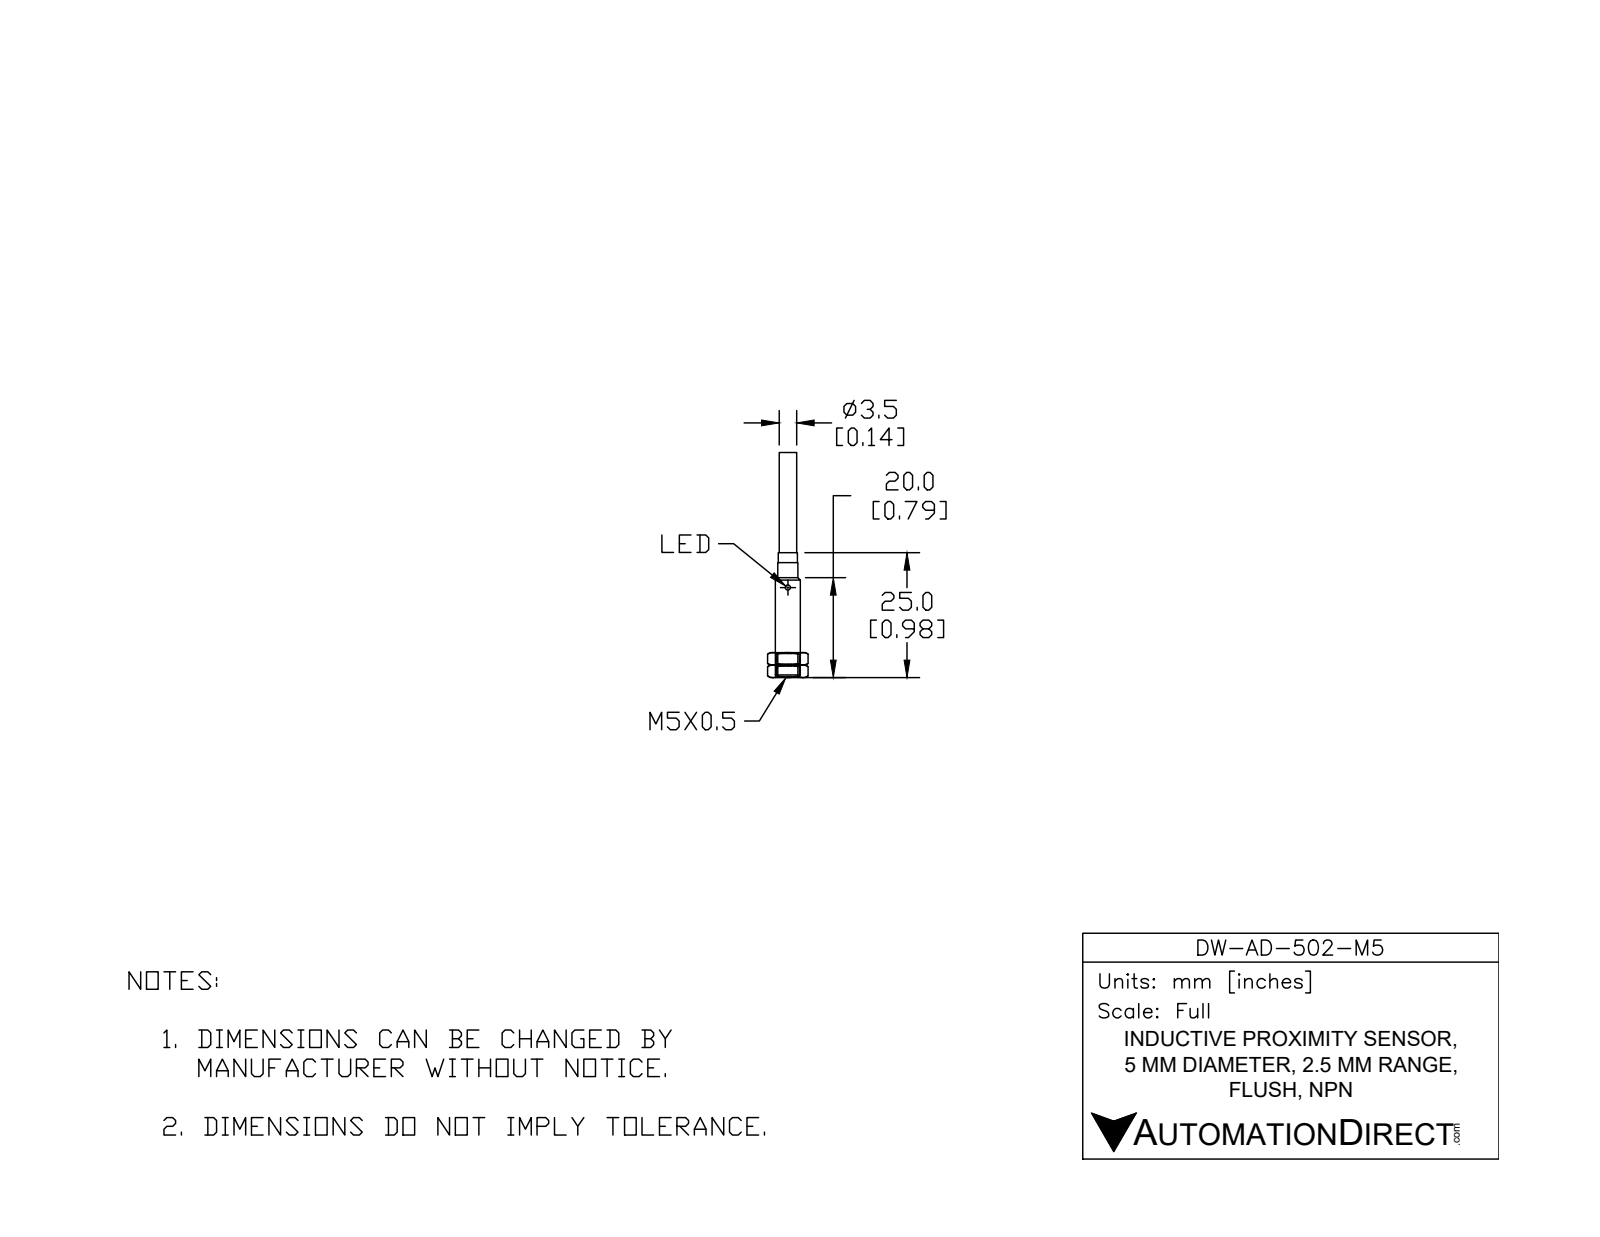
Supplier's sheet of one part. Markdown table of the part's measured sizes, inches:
| quantity | value |
| --- | --- |
| part name | DW-AD-502-M5 |
| STEP written by | SolidWorks 2017 (AUTOMOTIVE_DESIGN) |
| units | inches |
| bodies | 2 solids, 14 faces (4 planar, 6 cylindrical, 4 other) |
| overall size | 1.887 × 0.197 × 0.197 |
| volume | 0.029 in³ |
| surface area | 1.554 in² |
| round holes (diameter × count) | 0.059 × 1, 0.14 × 1 |
| round bosses / shafts (diameter × count) | 0.197 × 1, 0.165 × 1, 0.138 × 1 |
| main face-to-face distances | 0.03, 0.787, 0.757, 0.984, 0.954, 0.197 |
